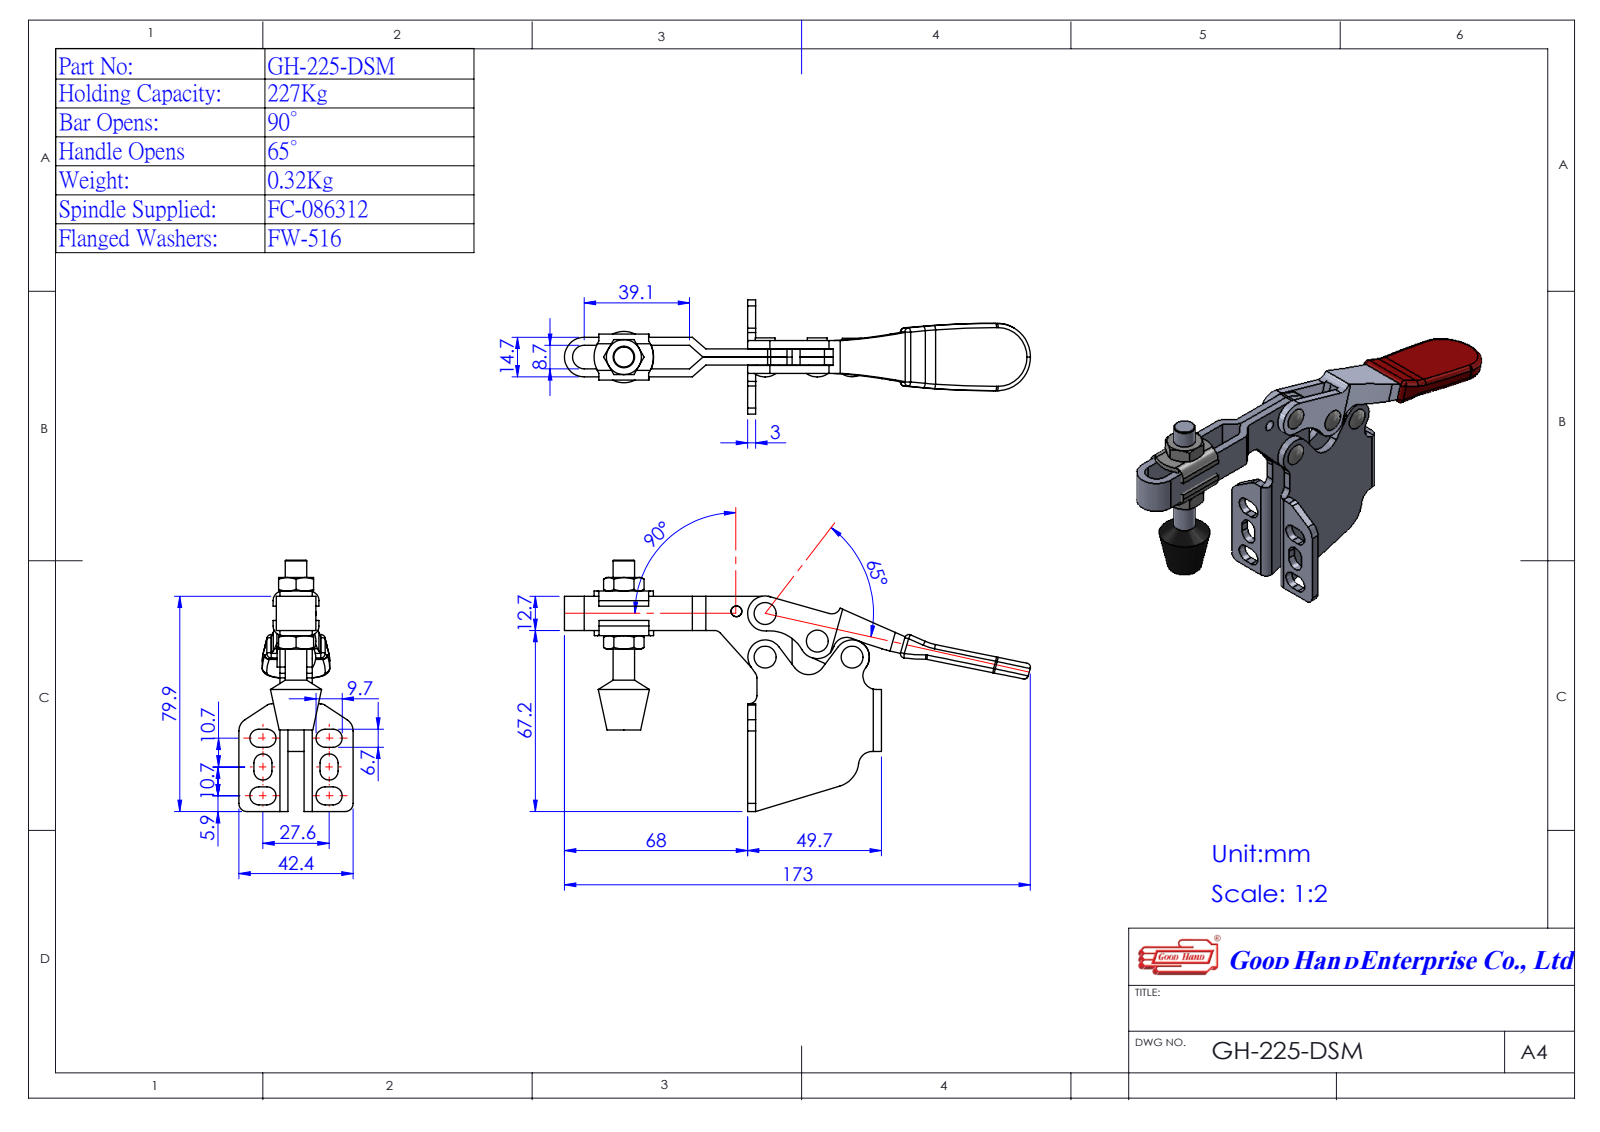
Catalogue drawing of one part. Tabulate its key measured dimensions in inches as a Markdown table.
| quantity | value |
| --- | --- |
| part name | Group1^GH-225-DSM(簡化)-1; 1225D05-1^GH-225-DSM(簡化)-1; Group1^GH-225-DSM(簡化); GH-225-DSM(簡化)-1 (+2 more) |
| STEP written by | SolidWorks 2016 (AUTOMOTIVE_DESIGN) |
| units | inches |
| bodies | 4 solids, 305 faces (136 planar, 142 cylindrical, 27 other) |
| overall size | 6.833 × 3.752 × 1.669 |
| volume | 2.173 in³ |
| surface area | 51.75 in² |
| round holes (diameter × count) | 0.197 × 4 |
| round bosses / shafts (diameter × count) | 0.289 × 4, 0.25 × 2, 0.248 × 2, 0.312 × 1, 0.197 × 1, 0.157 × 1 |
| partial cylindrical surfaces (radius × count) | 0.132 × 12, 0.118 × 11, 0.047 × 4, 0.142 × 4, 0.197 × 4, 0.435 × 4, 0.252 × 3, 0.256 × 3 |
| main face-to-face distances | 0.118, 0.236, 0.354, 0.472, 0.122, 0.24, 0.358, 0.237, 0.119, 0.118 |
| hole center spacings | 0.561, 0.638, 0.777, 0.866, 1.272, 1.422 |
